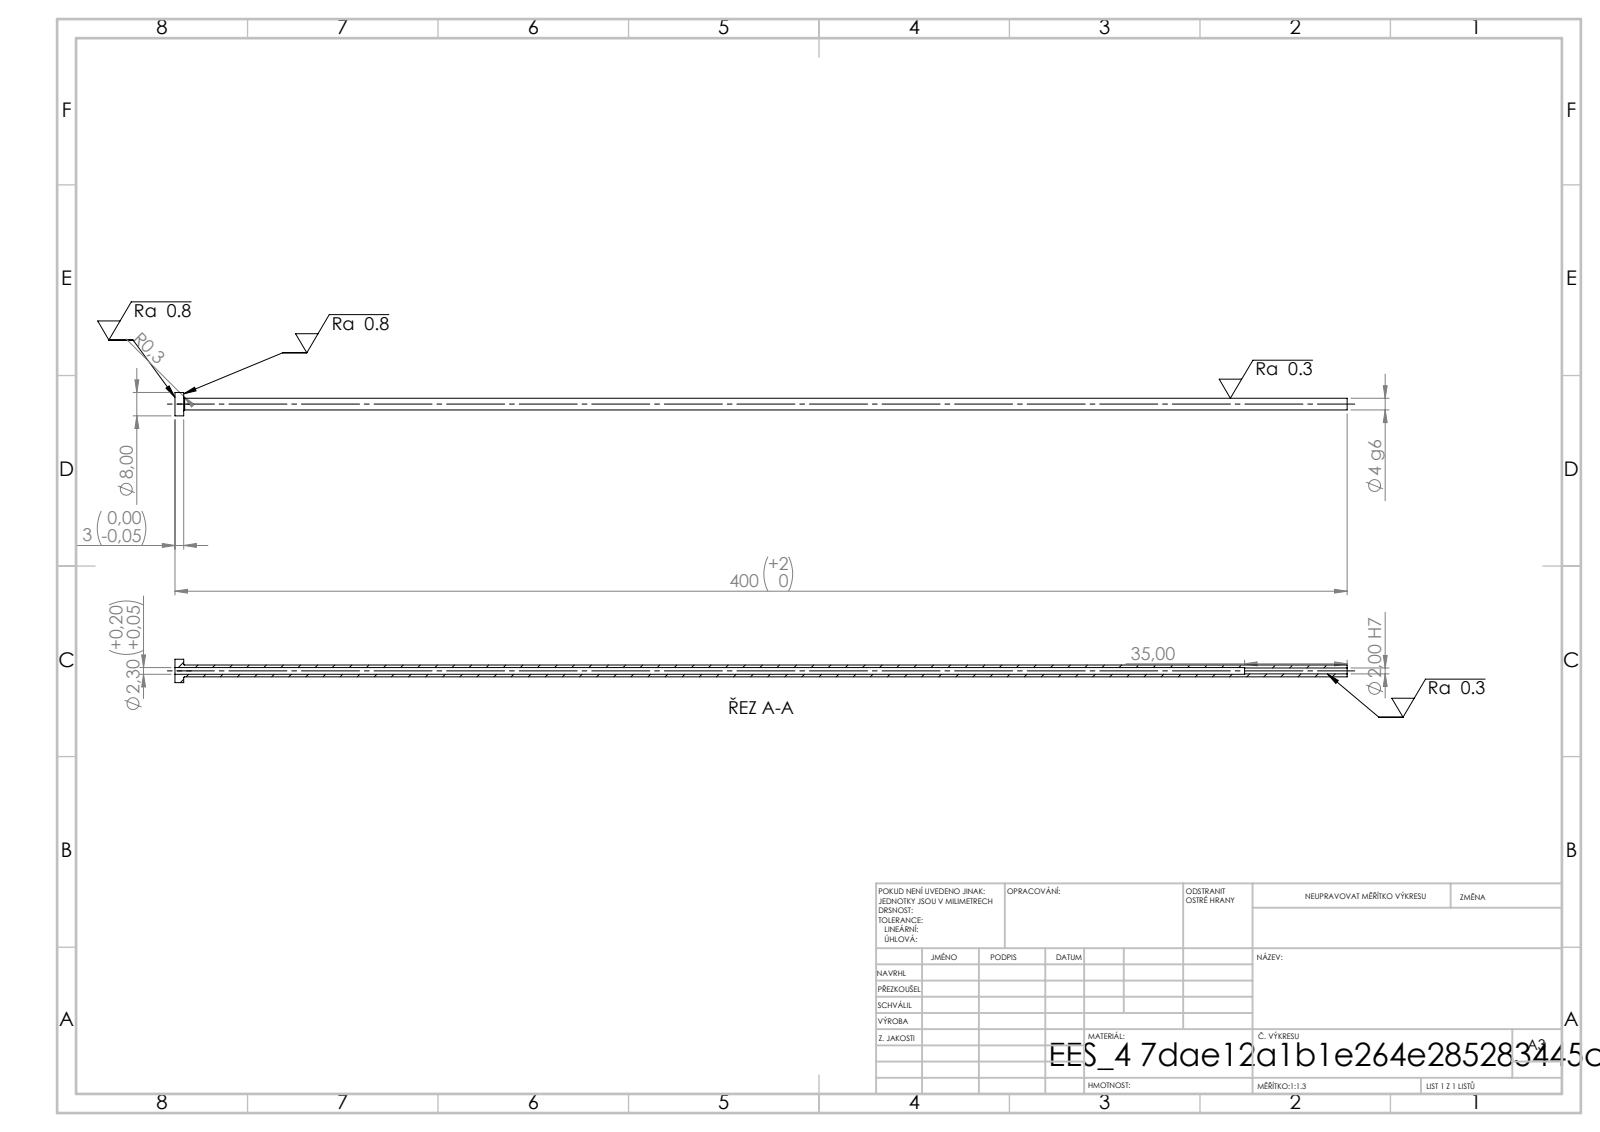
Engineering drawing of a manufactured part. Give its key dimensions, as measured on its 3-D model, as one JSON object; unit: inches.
{"step_written_by": "SolidWorks 2019 (CONFIG_CONTROL_DESIGN)", "units": "inches", "bodies": {"solids": 1, "faces": 14, "planar": 4, "cylindrical": 8, "other": 2}, "overall_size": [15.748, 0.315, 0.315], "volume_in3": 0.214, "surface_area_in2": 12.42, "round_holes": [[0.079, 1], [0.091, 1]], "round_bosses_or_shafts": [[0.315, 1], [0.157, 1]], "face_to_face_distances": [0.118, 15.748, 15.63, 14.37, 14.252, 1.378]}
